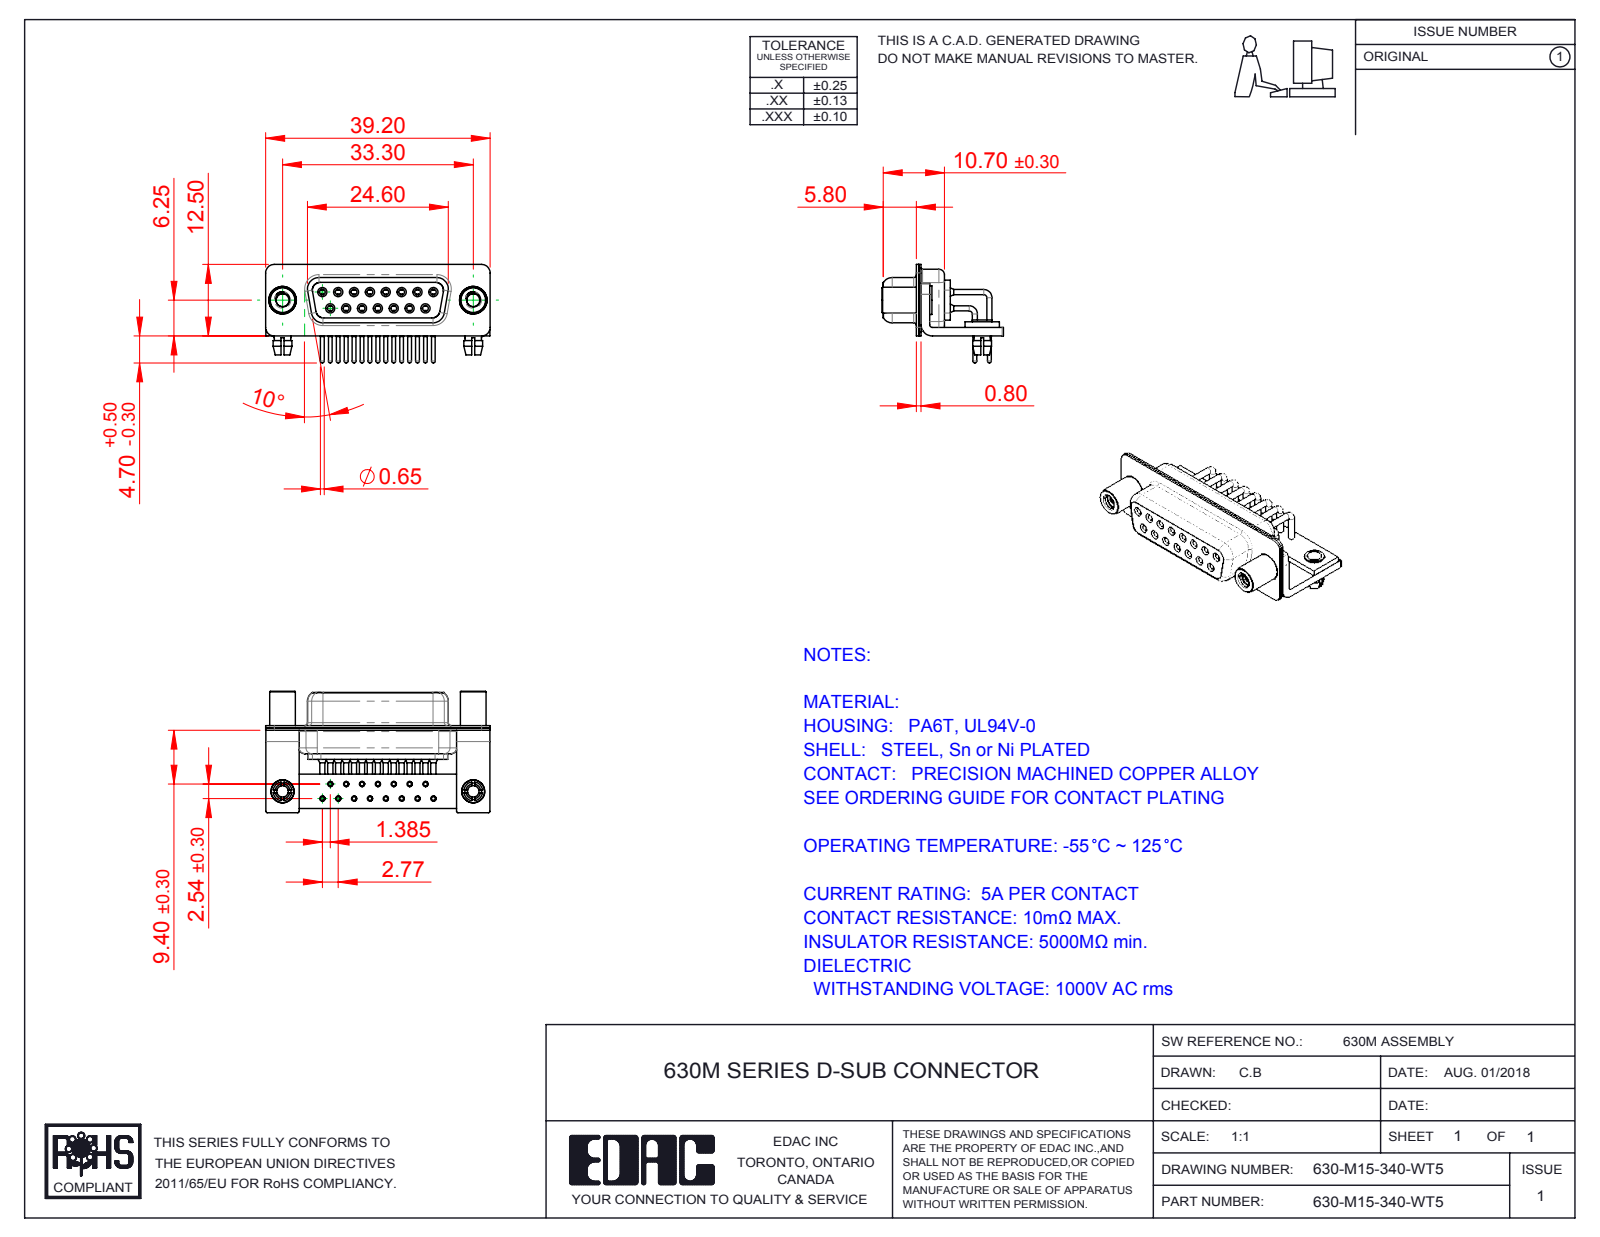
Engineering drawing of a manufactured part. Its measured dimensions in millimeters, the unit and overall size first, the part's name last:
Units: millimetres
Overall size (bounding box): 39.2 × 21.2 × 17.2
Round holes (diameter × count): ⌀2 ×17, ⌀0.9 ×15, ⌀1 ×15, ⌀1.1 ×15, ⌀1.7 ×15, ⌀1.8 ×15, ⌀2.26 ×2, ⌀2.5 ×2, ⌀3.2 ×2, ⌀4 ×2, ⌀4.8 ×2
Round bosses / shafts (diameter × count): ⌀0.9 ×27, ⌀1.6 ×15, ⌀1.5 ×15, ⌀0.65 ×15, ⌀5 ×2, ⌀4.9 ×2, ⌀4.5 ×2, ⌀4 ×2
Partial cylindrical surfaces — rounded edges, fillets, slot ends (radius × count): R0.25 ×16, R1.5 ×16, R2 ×13, R1.35 ×8, R1.6 ×8, R0.5 ×5, R0.6 ×4, R0.65 ×4
Main face-to-face distances: 0.4, 2.3, 1.9, 0.8, 1.5, 9.35, 1, 1.45, 8.95, 0.85
Hole centre spacings: 2.77, 5.54, 8.31, 3.16, 4.87, 11.08, 2.89, 7.37
Volume: 3 217 mm³ · Surface area: 8 278 mm²
Bodies: 25 solids, 1296 faces (368 planar, 608 cylindrical, 320 other)
Part name (STEP PRODUCT): 630M Housing_15 Contacts; 630-M15-340-WT5; 630M Stabilizer Board_15 Contacts; 630M Shell Rear_15 Contacts (+6 more)
STEP written by: SolidWorks 2016 (CONFIG_CONTROL_DESIGN)
